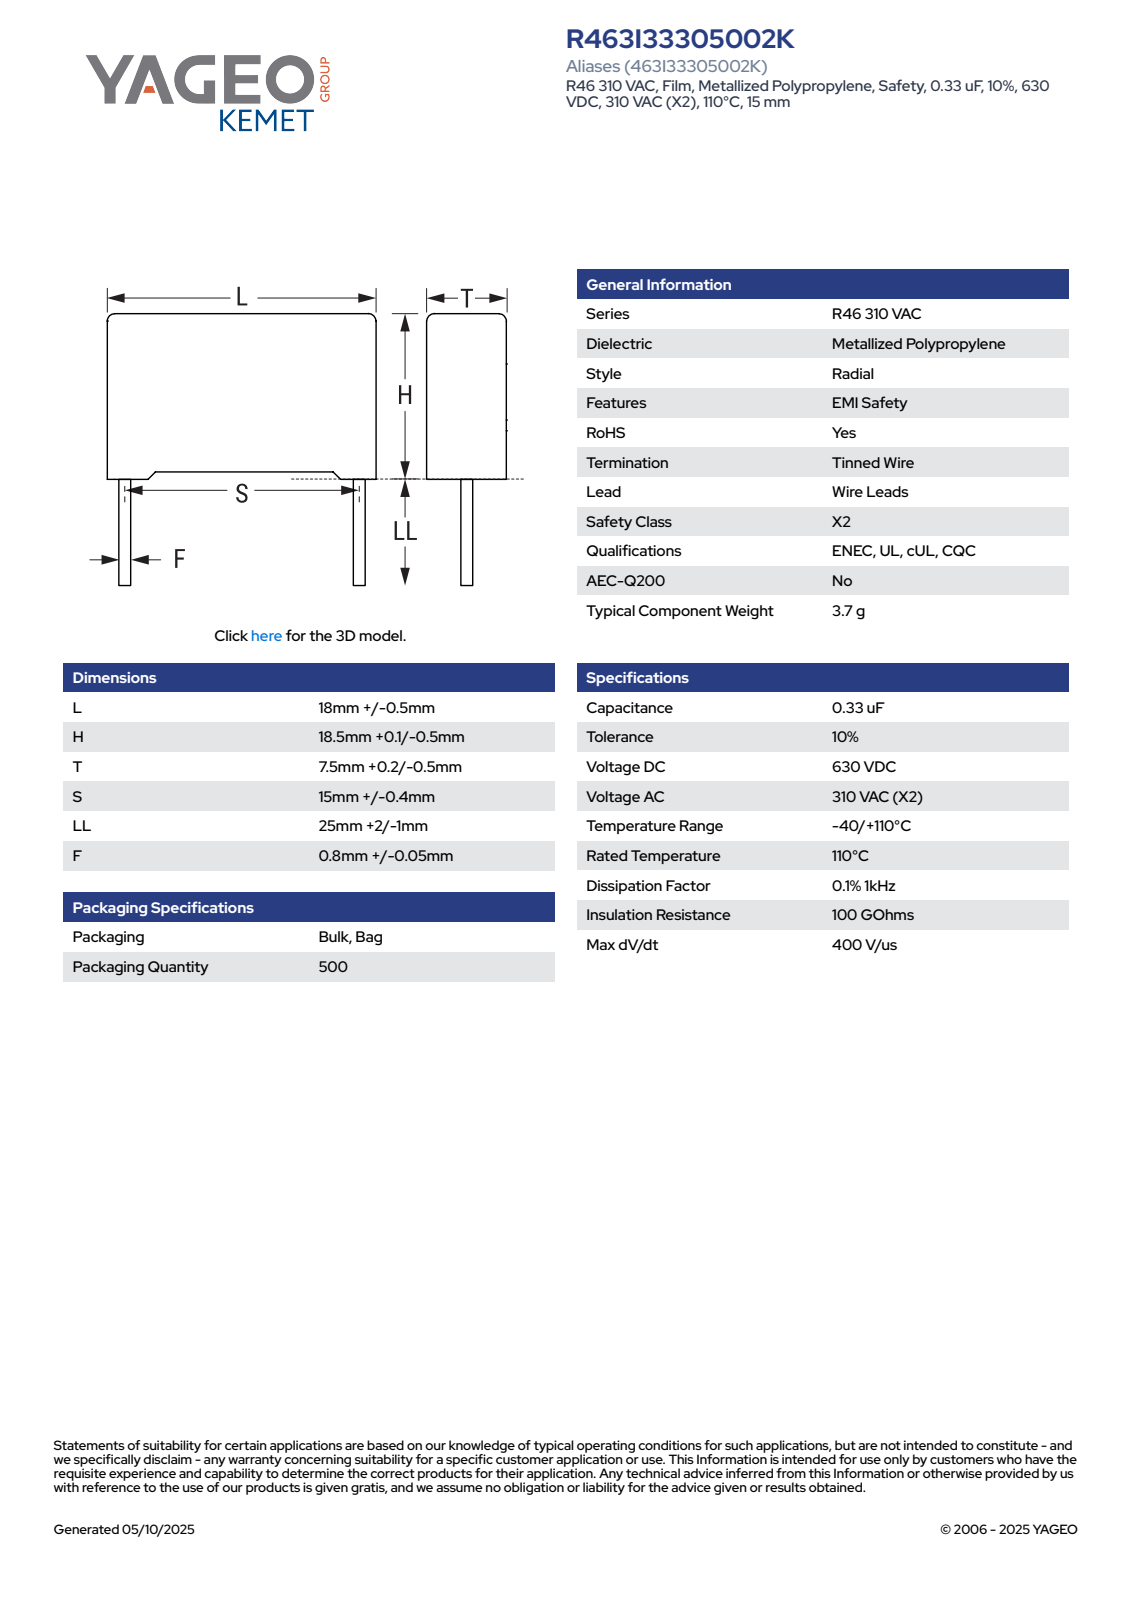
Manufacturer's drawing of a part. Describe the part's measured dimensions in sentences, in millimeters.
The part is named "CFR_RB2_18X18.5X7.5_L18.5H18.6T7.7S15LL27F0.85". Its 3-D file was written by "SolidWorks 2021 (AUTOMOTIVE_DESIGN)". It is 4 solids with 85 faces: 77 planar, 8 cylindrical and 0 other. Overall it measures 45.6 by 18.5 by 7.71 millimeters. Its volume is 2 586 cubic millimeters and its surface area 1 429 square millimeters. Round bosses or shafts: 2 of diameter 0.85. Partial cylindrical surfaces (rounded edges, fillets, slot ends): 4 of radius 0.5. The main face-to-face distances are 7.7, 18.5, 17.85, 0.62, 0.75, 18.6, 0.64, 17.96, 7.08, 17.88.
